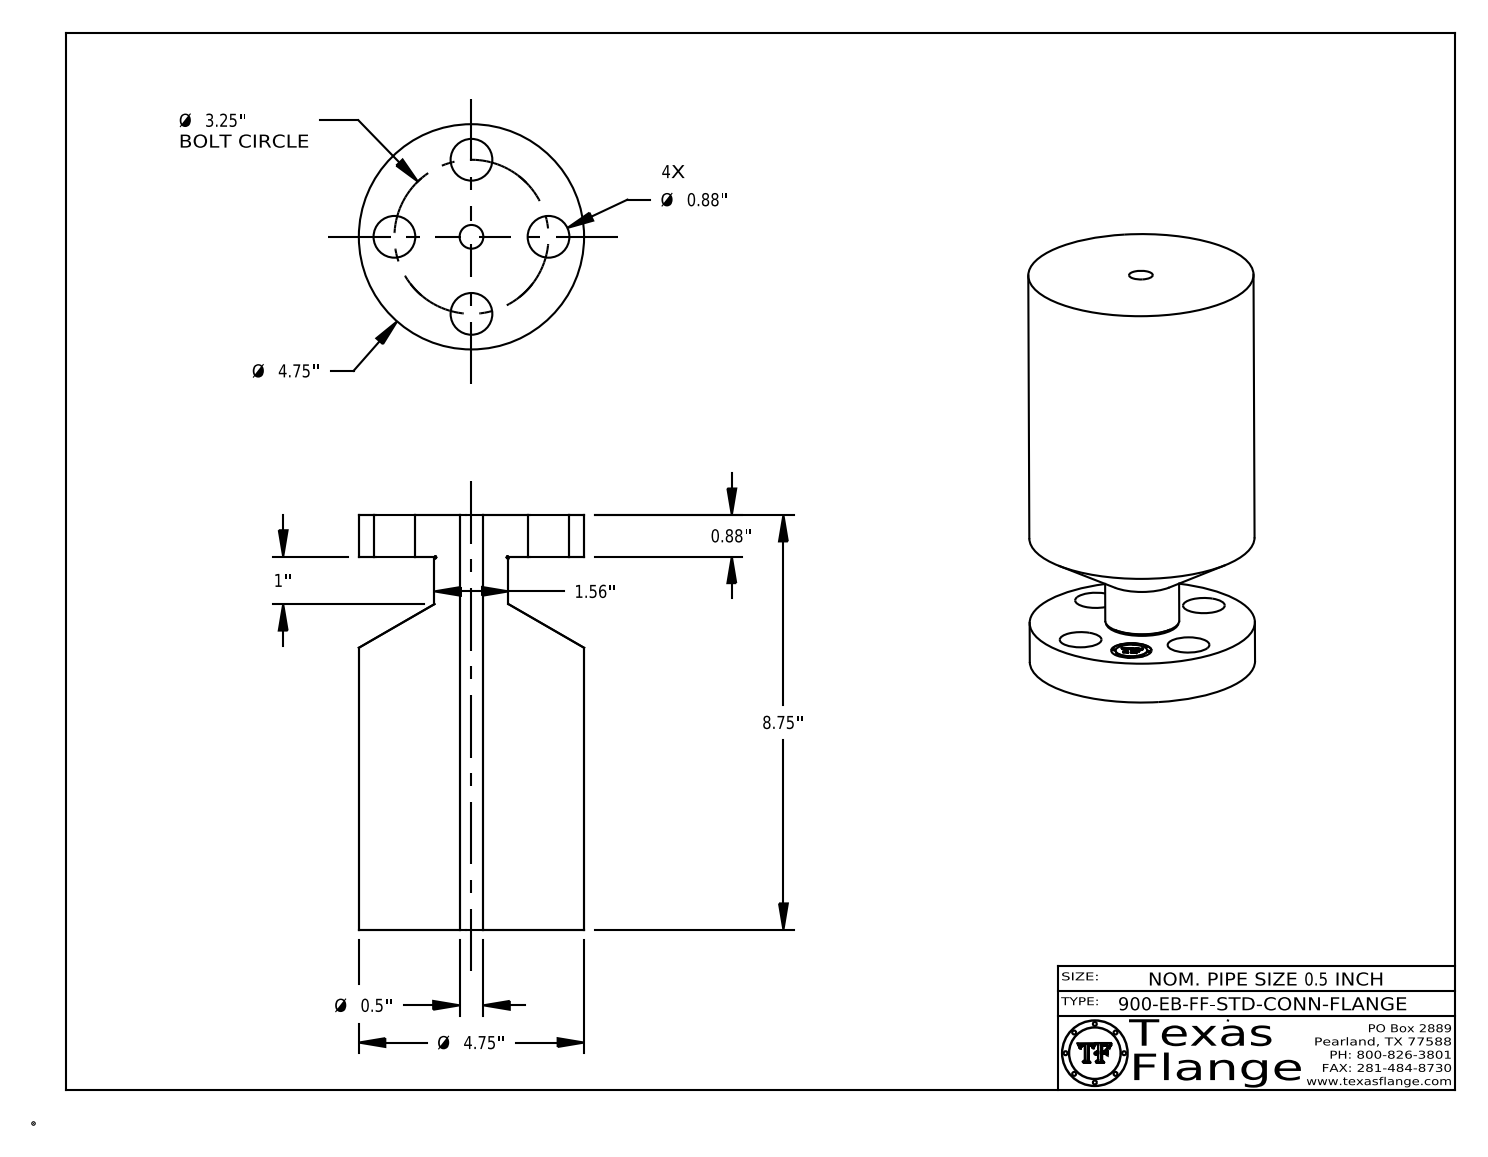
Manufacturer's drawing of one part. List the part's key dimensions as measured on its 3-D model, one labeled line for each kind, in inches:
Part name (STEP PRODUCT): 0.5-900-EB-FF-STD-CONN-FLANGE
STEP written by: CATIA V5 STEP AP214 (AUTOMOTIVE_DESIGN)
Units: inches
Bodies: 1 solid, 410 faces (368 planar, 36 cylindrical, 6 other)
Overall size (bounding box): 8.75 × 4.75 × 4.75
Volume: 126.9 in³ · Surface area: 194.8 in²
Round holes (diameter × count): ⌀0.88 ×4, ⌀0.5 ×1, ⌀0.85 ×1
Round bosses / shafts (diameter × count): ⌀0.051 ×8, ⌀4.75 ×1, ⌀1.56 ×1, ⌀0.67 ×1
Main face-to-face distances: 8.75, 0.88, 7.87, 0.875, 7.875, 0.254, 0.248, 0.016, 0.046, 0.165
Hole centre spacings: 1.625, 2.298, 1.244, 3.003, 3.25
